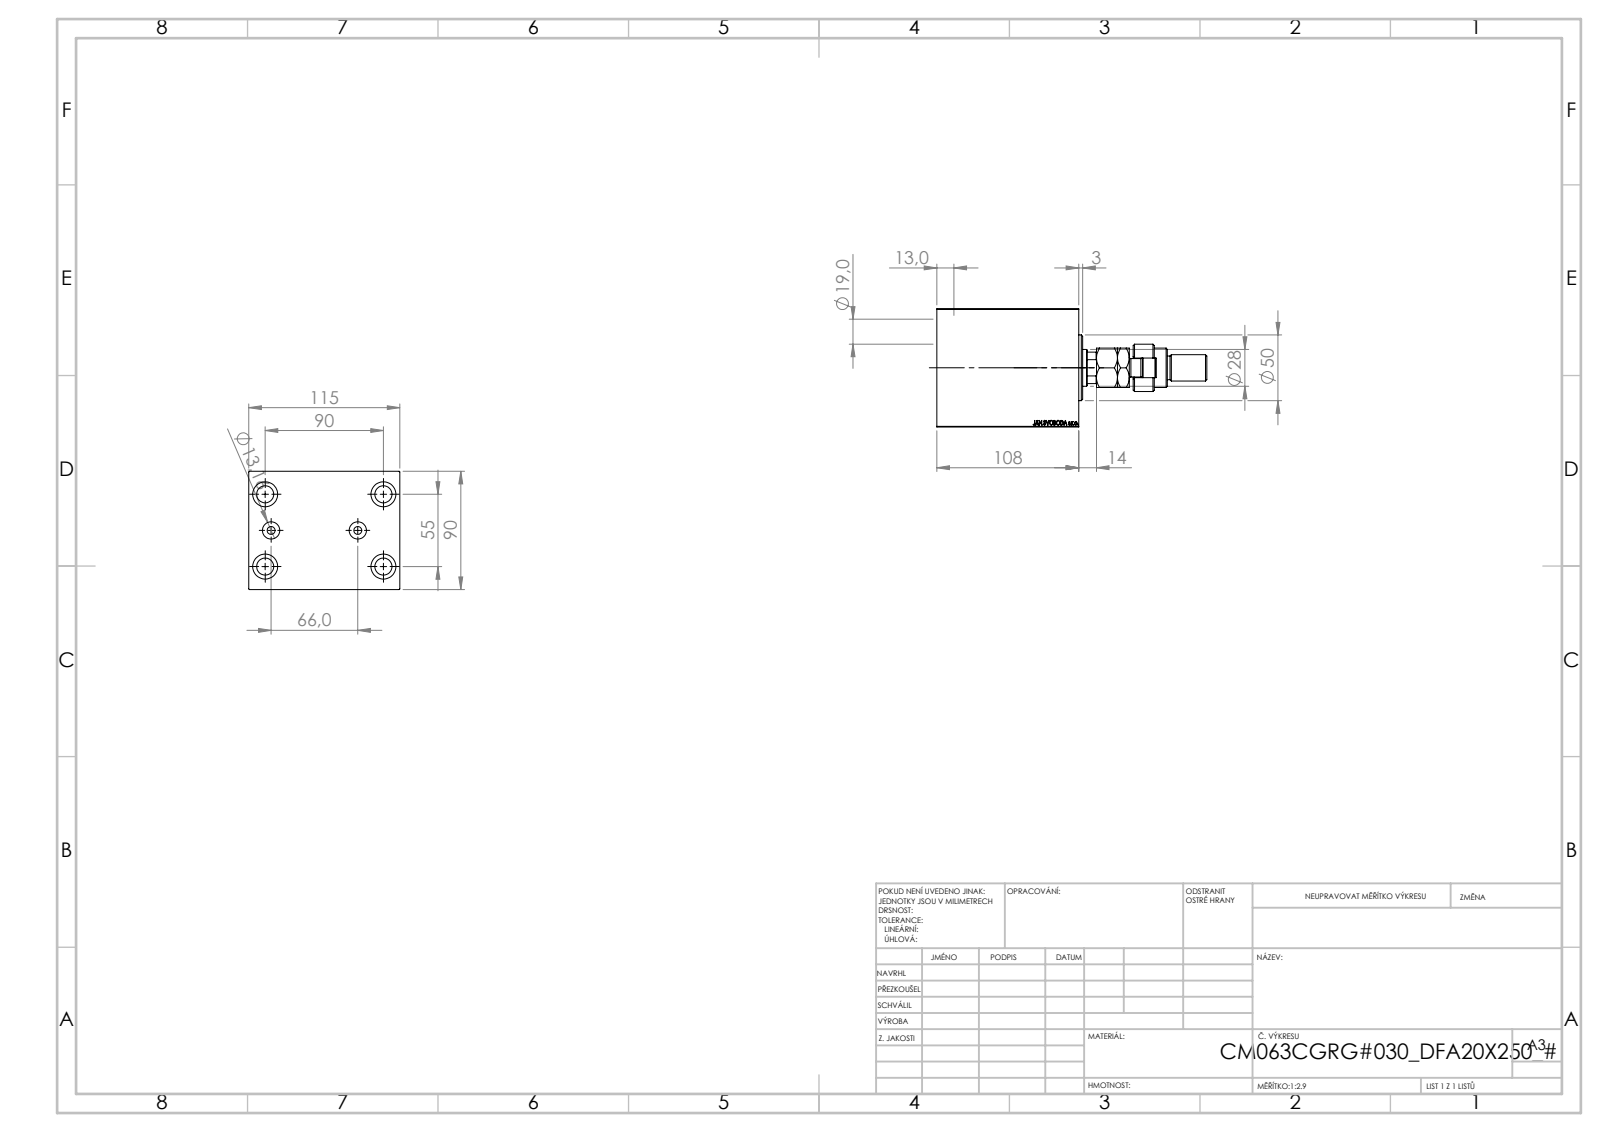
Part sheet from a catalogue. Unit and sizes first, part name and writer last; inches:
Units: inches
Overall size (bounding box): 8.091 × 4.528 × 3.543
Round holes (diameter × count): ⌀0.512 ×4, ⌀0.748 ×4, ⌀0.236 ×2, ⌀0.518 ×2, ⌀0.728 ×1, ⌀1.102 ×1, ⌀1.24 ×1, ⌀2.48 ×1, ⌀2.559 ×1, ⌀2.835 ×1
Round bosses / shafts (diameter × count): ⌀1.969 ×1, ⌀1.417 ×1, ⌀1.181 ×1, ⌀0.866 ×1, ⌀0.787 ×1, ⌀0.709 ×1, ⌀0.551 ×1
Partial cylindrical surfaces — rounded edges, fillets, slot ends (radius × count): R0.295 ×1, R0.472 ×1, R0.531 ×1
Main face-to-face distances: 3.543, 4.528, 4.252, 0.748, 3.504, 1.181, 1.154, 2.35, 3.098, 2.335
Hole centre spacings: 1.181, 2.076, 3.256, 1.299, 2.165, 3.543, 4.153, 2.598
Volume: 62 in³ · Surface area: 237.1 in²
Bodies: 5 solids, 946 faces (437 planar, 71 cylindrical, 438 other)
Part name (STEP PRODUCT): V450CM_C_VCP; FEMALE_PART_FOR_DFA; V450CM_VC_B; MFA (+1 more)
STEP written by: SolidWorks 2019 (CONFIG_CONTROL_DESIGN)
